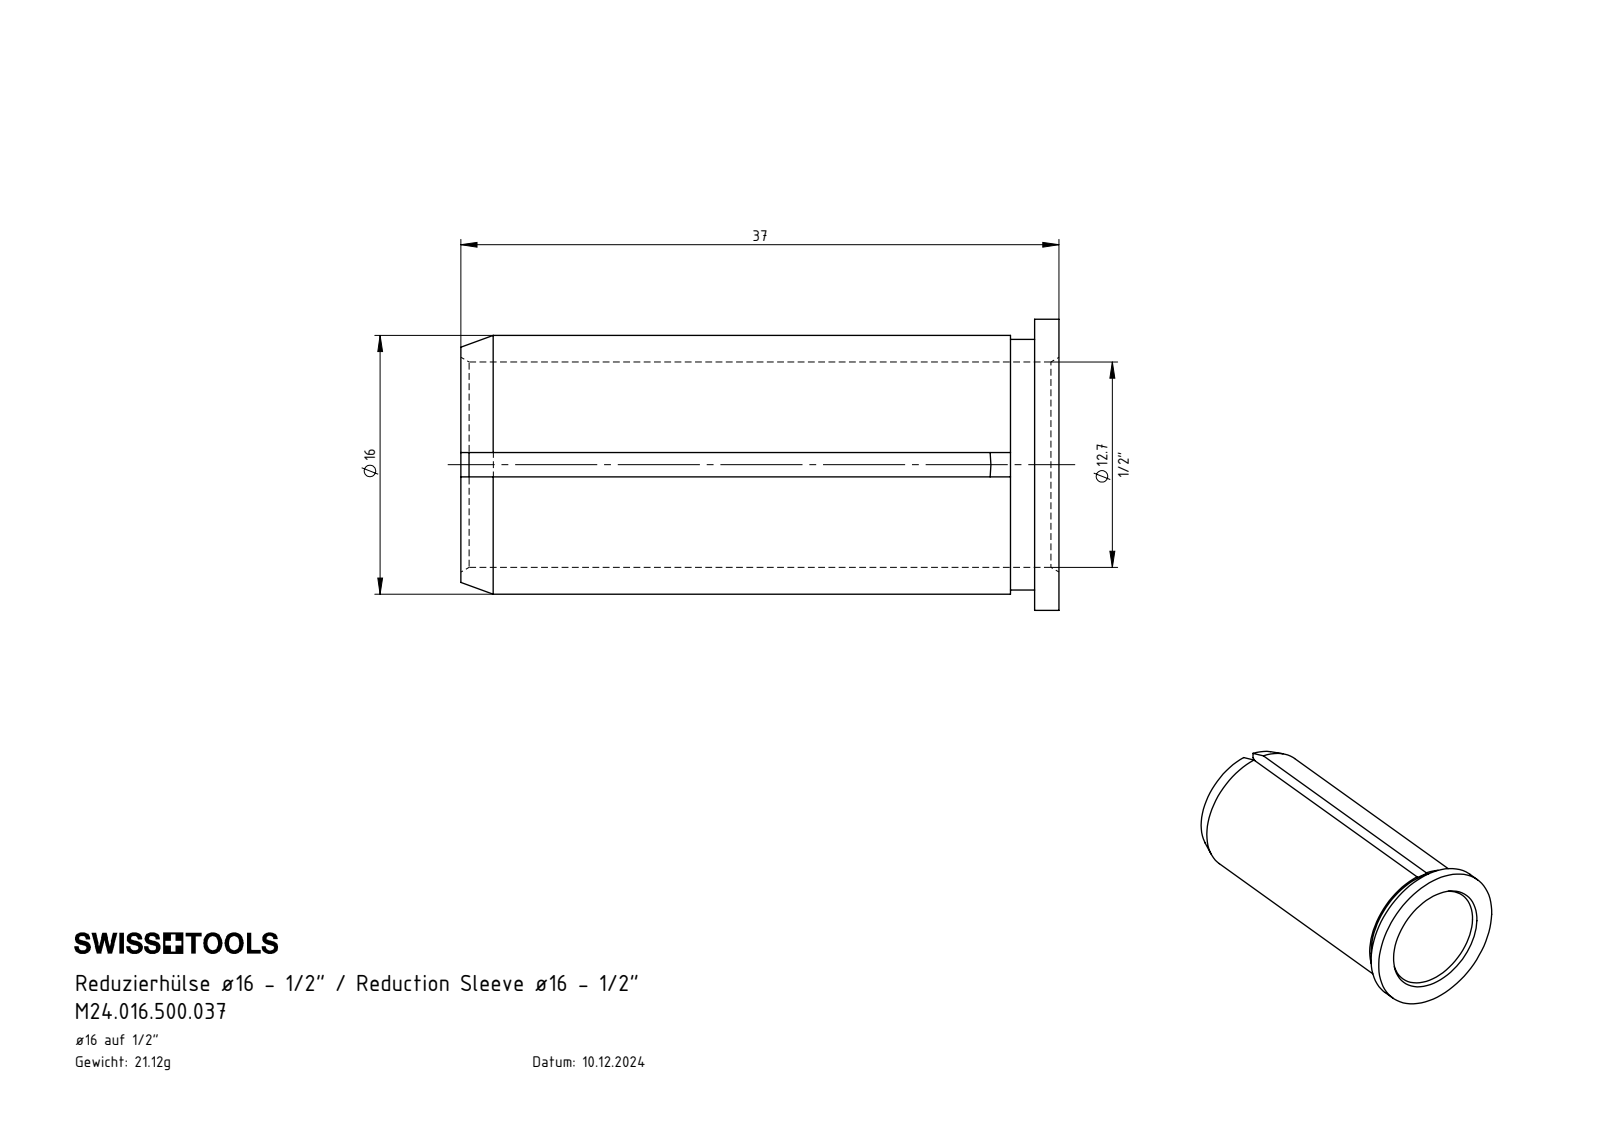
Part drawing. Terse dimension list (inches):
name: M24.016.500.037
written by: SolidWorks 2022 (CONFIG_CONTROL_DESIGN)
unit: in
bodies: 1 solid, 24 faces (6 planar, 10 cylindrical, 8 other)
size: 1.457 × 0.709 × 0.709
volume: 0.164 in³; area: 5.555 in²
holes: 1× ⌀0.5
bosses: 1× ⌀0.709, 1× ⌀0.63, 1× ⌀0.61
rounds: 1× R1.24
face distances: 0.059, 1.398, 1.457, 1.339, 0.118
